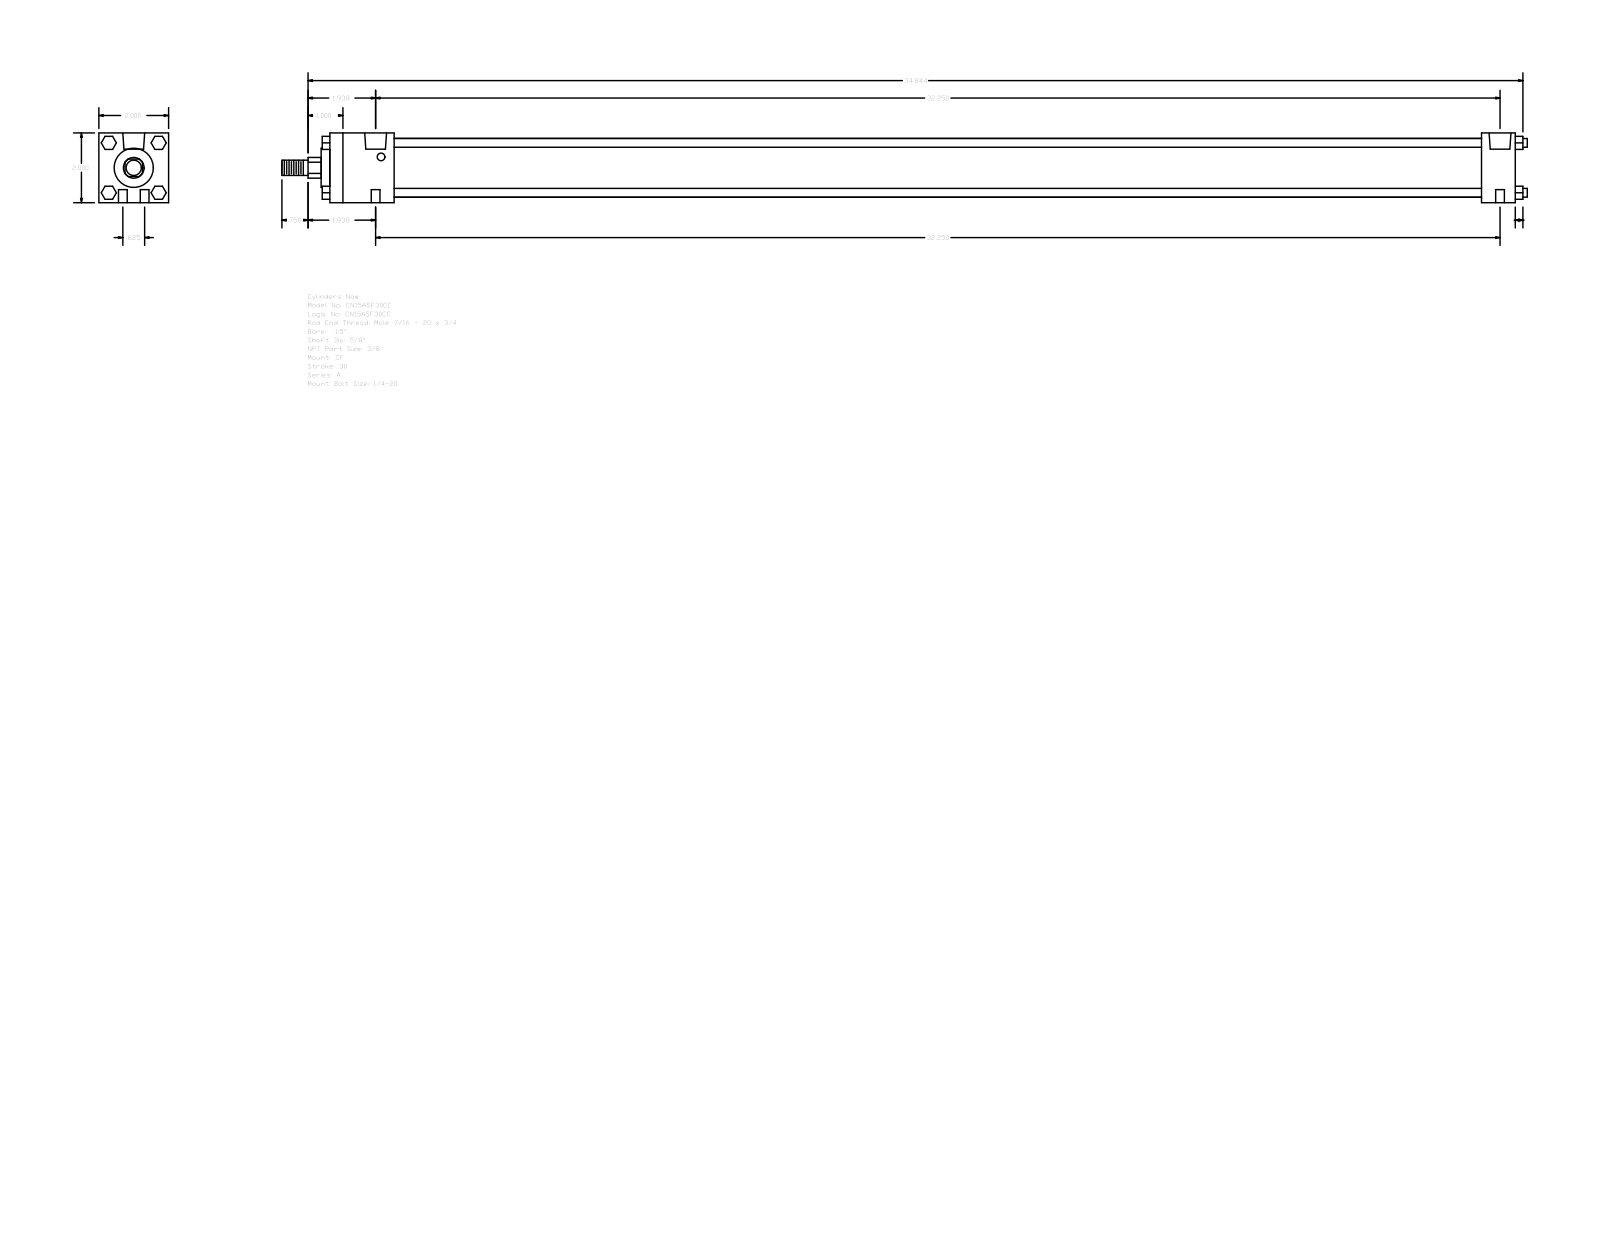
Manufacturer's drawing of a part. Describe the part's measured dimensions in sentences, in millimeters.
The part is named "A_SF__0150_0.625". Its 3-D file was written by "GSSL Pune (CONFIG_CONTROL_DESIGN)". It is 0 solids with 124 faces: 94 planar, 30 cylindrical and 0 other. Overall it measures 907.26 by 50.8 by 50.8 millimeters. Round holes: 4 of diameter 6.35, 2 of diameter 5.56, 2 of diameter 15.93. Round bosses or shafts: 4 of diameter 6.35, 1 of diameter 42.93, 1 of diameter 28.57, 1 of diameter 15.88, 1 of diameter 11.11. Partial cylindrical surfaces (rounded edges, fillets, slot ends): 1 of radius 7.54. The main face-to-face distances are 50.8, 863.6, 46.83, 838.99, 792.16, 816.77, 24.61, 6.35, 9.52, 53.18. The hole center spacings are 7.94, 819.19, 819.15, 15.88, 819.3, 811.21.
